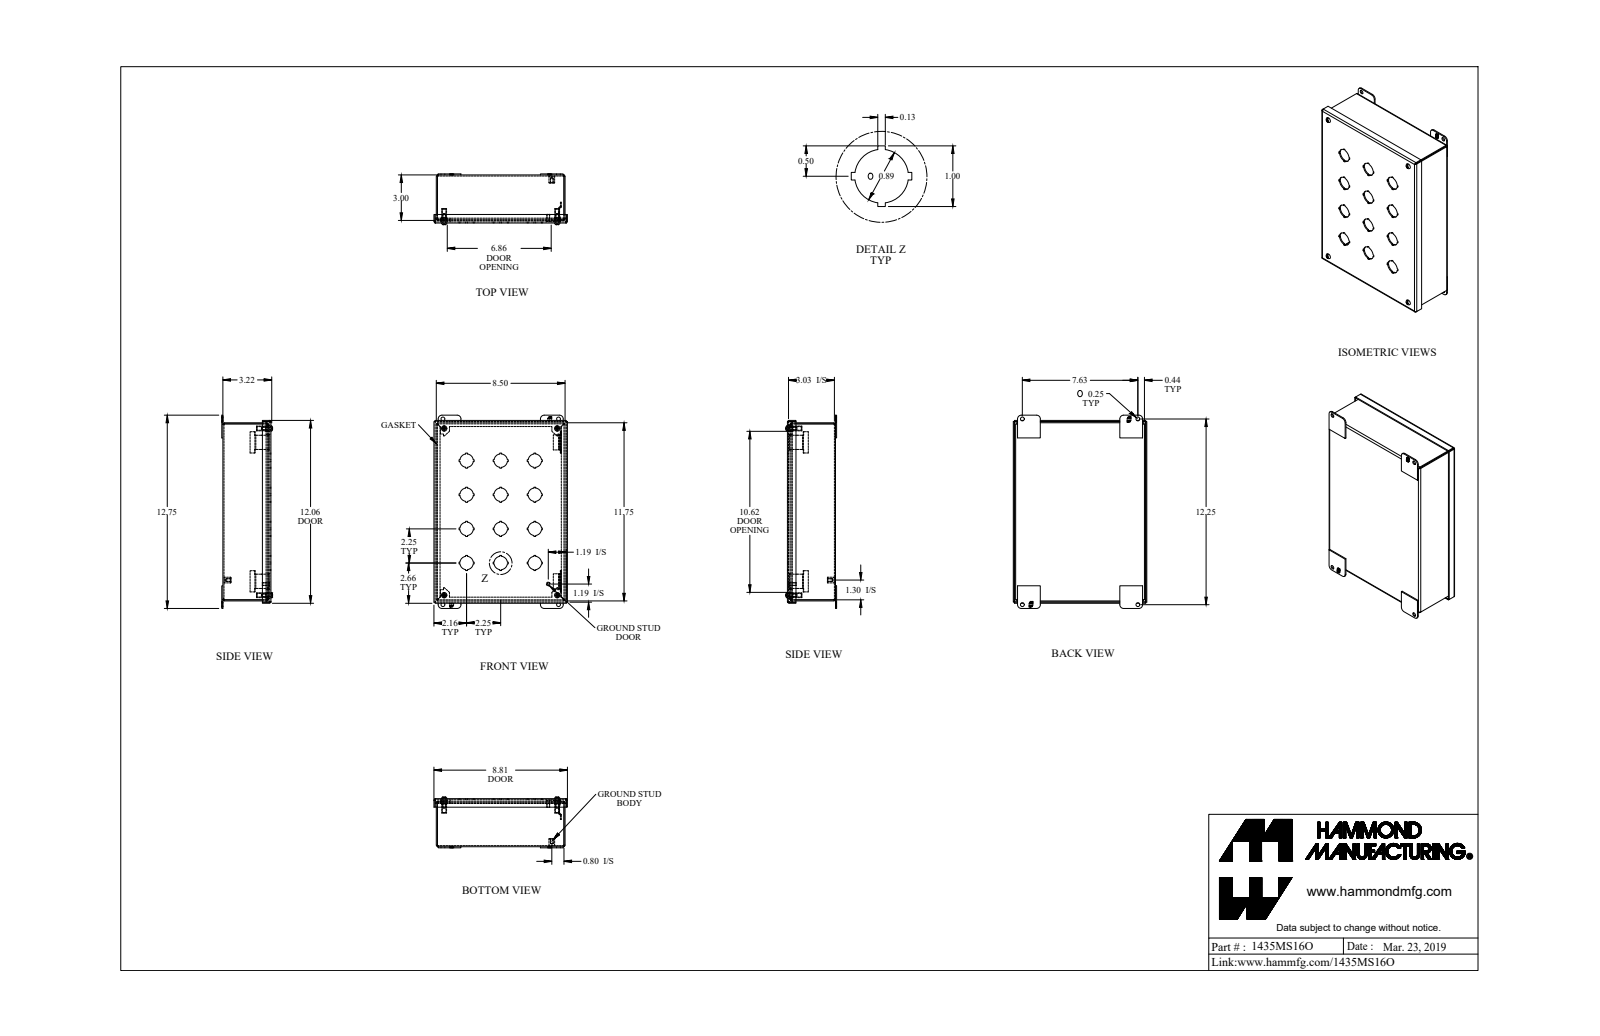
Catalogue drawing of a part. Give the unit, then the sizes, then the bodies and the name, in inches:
Units: inches
Overall size (bounding box): 12.75 × 8.81 × 3.354
Round holes (diameter × count): ⌀0.886 ×12, ⌀0.25 ×8, ⌀0.065 ×4, ⌀0.239 ×4, ⌀0.253 ×4, ⌀0.406 ×4, ⌀0.156 ×1
Round bosses / shafts (diameter × count): ⌀0.19 ×5, ⌀0.406 ×4, ⌀0.315 ×4, ⌀0.148 ×4, ⌀0.375 ×1, ⌀0.25 ×1
Partial cylindrical surfaces — rounded edges, fillets, slot ends (radius × count): R0.036 ×12, R0.108 ×12, R0.25 ×8, R0.029 ×4, R0.086 ×4, R0.171 ×4
Main face-to-face distances: 0.072, 3.1, 3.172, 3.028, 8.428, 0.072, 11.678, 8.5, 8.356, 0.155
Hole centre spacings: 2.25, 5.031, 3.182, 4.5, 7.46, 7.461, 7.569, 10.999
Volume: 29.39 in³ · Surface area: 780.7 in²
Bodies: 23 solids, 797 faces (567 planar, 200 cylindrical, 30 other)
Part name (STEP PRODUCT): 1435MS16O_Default
STEP written by: SolidWorks 2019 (CONFIG_CONTROL_DESIGN)
